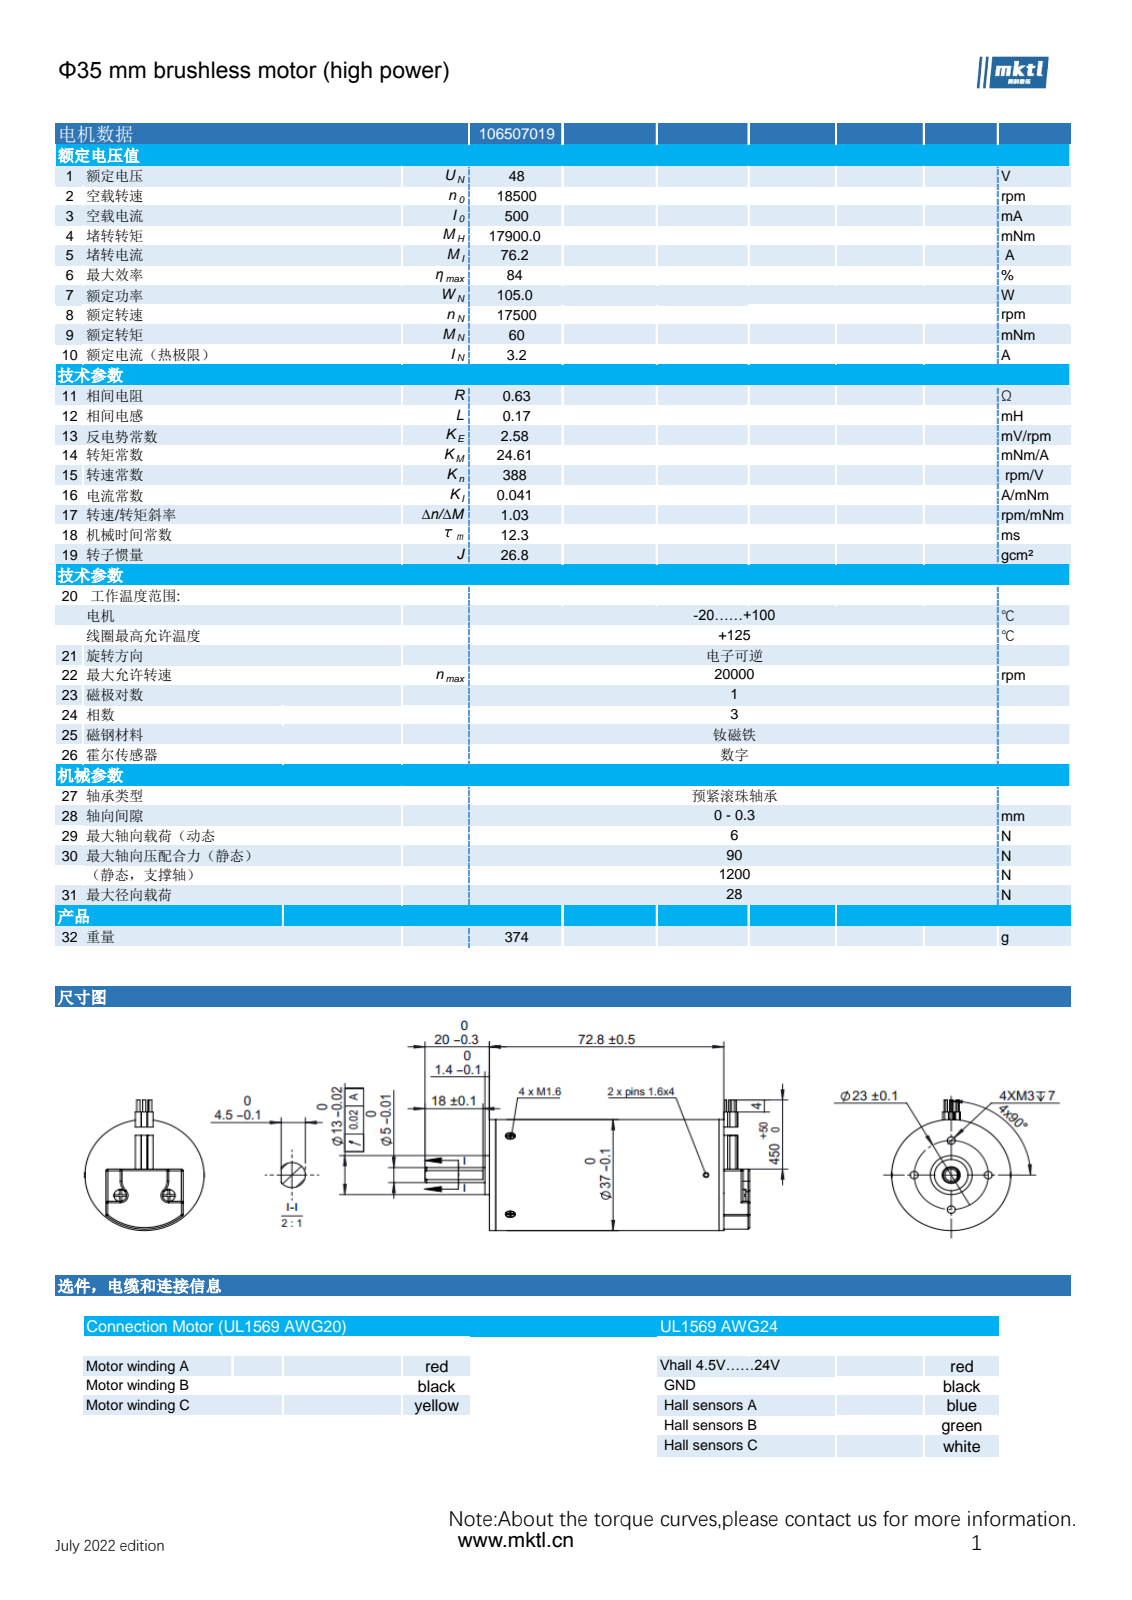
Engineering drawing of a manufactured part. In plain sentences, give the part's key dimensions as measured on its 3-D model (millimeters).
The part is named "106507019". Its 3-D file was written by "SolidWorks 2025 (AUTOMOTIVE_DESIGN)". It is 346 solids with 3585 faces: 1420 planar, 1860 cylindrical and 305 other. Overall it measures 100.8 by 43.5 by 37 millimeters. Its volume is 75 388 cubic millimeters and its surface area 270 800 square millimeters. Round holes: 6 of diameter 2.1, 5 of diameter 0.75, 4 of diameter 1, 4 of diameter 2.5, 3 of diameter 1.5, 3 of diameter 1.6, 3 of diameter 3, 2 of diameter 1.2, 2 of diameter 1.65, 2 of diameter 2.05, 2 of diameter 3.1, 1 of diameter 1.3. Round bosses or shafts: 16 of diameter 1.2, 12 of diameter 1.8, 12 of diameter 0.5, 6 of diameter 0.58, 5 of diameter 4, 5 of diameter 1.6, 5 of diameter 0.6, 3 of diameter 1. Partial cylindrical surfaces (rounded edges, fillets, slot ends): 24 of radius 0.1, 18 of radius 0.5, 11 of radius 0.75, 10 of radius 1, 8 of radius 0.42, 7 of radius 0.6, 3 of radius 0.3, 2 of radius 1.9. The main face-to-face distances are 0.4, 0.6, 1, 0.8, 1.2, 1.4, 1.6, 1.8, 2, 15. The hole center spacings are 2, 2.3, 11.5, 13.25, 16.26, 18.78, 23, 23.79.
